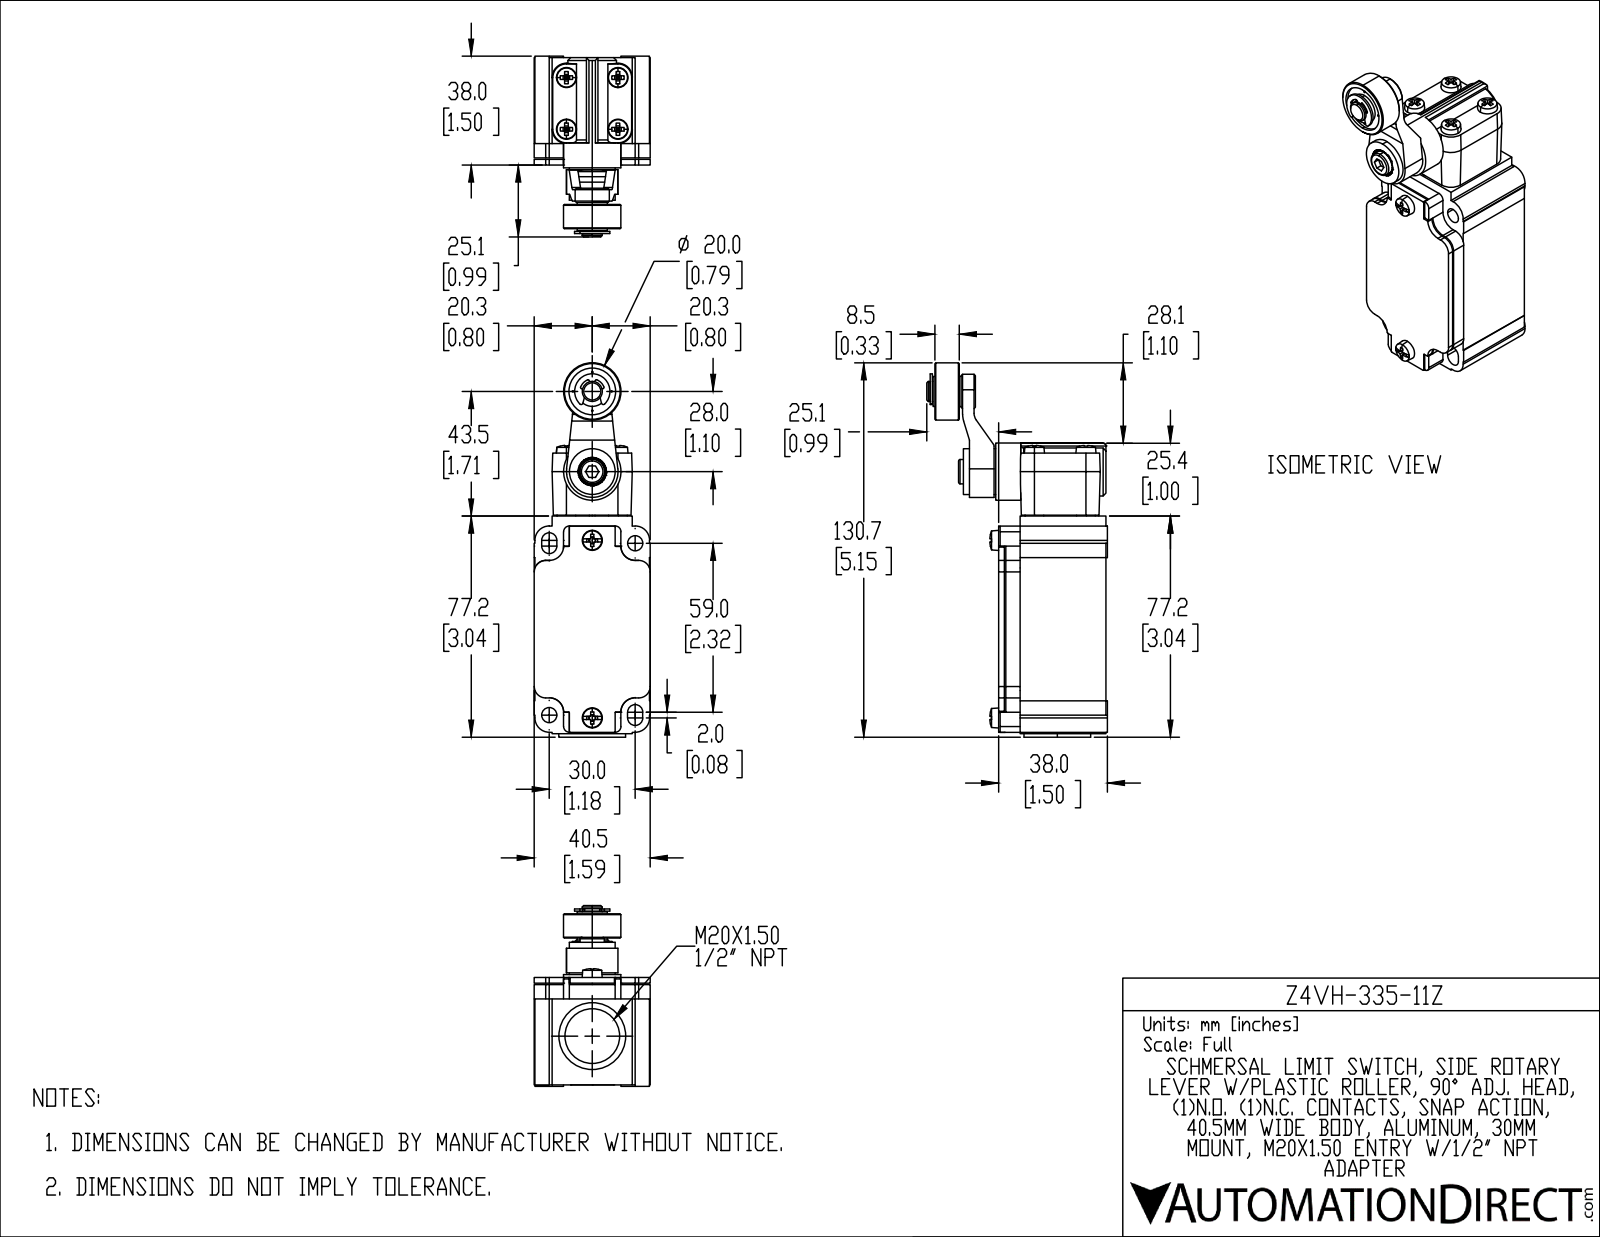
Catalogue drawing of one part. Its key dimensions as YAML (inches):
part_name: "Z4VH-335-11Z"
step_written_by: "SolidWorks 2019 (AUTOMOTIVE_DESIGN)"
units: inches
bodies: {solids: 1, faces: 1021, planar: 613, cylindrical: 299, other: 109}
overall_size: [5.146, 2.484, 1.594]
volume: 7.893
surface_area: 45.74
round_holes:
  - {diameter: 0.02, count: 4}
  - {diameter: 0.209, count: 2}
  - {diameter: 0.224, count: 1}
  - {diameter: 0.642, count: 1}
  - {diameter: 0.75, count: 1}
round_bosses_or_shafts:
  - {diameter: 0.787, count: 2}
  - {diameter: 0.079, count: 2}
  - {diameter: 0.917, count: 1}
  - {diameter: 0.709, count: 1}
  - {diameter: 0.669, count: 1}
  - {diameter: 0.63, count: 1}
  - {diameter: 0.413, count: 1}
  - {diameter: 0.335, count: 1}
partial_cylinders:
  - {radius: 0.008, count: 72}
  - {radius: 0.006, count: 36}
  - {radius: 0.1, count: 16}
  - {radius: 0.157, count: 13}
  - {radius: 0.01, count: 12}
  - {radius: 0.197, count: 12}
  - {radius: 0.079, count: 4}
  - {radius: 0.104, count: 4}
face_to_face_distances: [0.02, 1.398, 0.079, 1.378, 1.476, 0.098, 1.181, 0.295, 1.594, 0.197]
hole_center_spacings: [0.266, 0.376, 0.531, 1.914, 2.112, 2.169, 2.256, 2.425]
